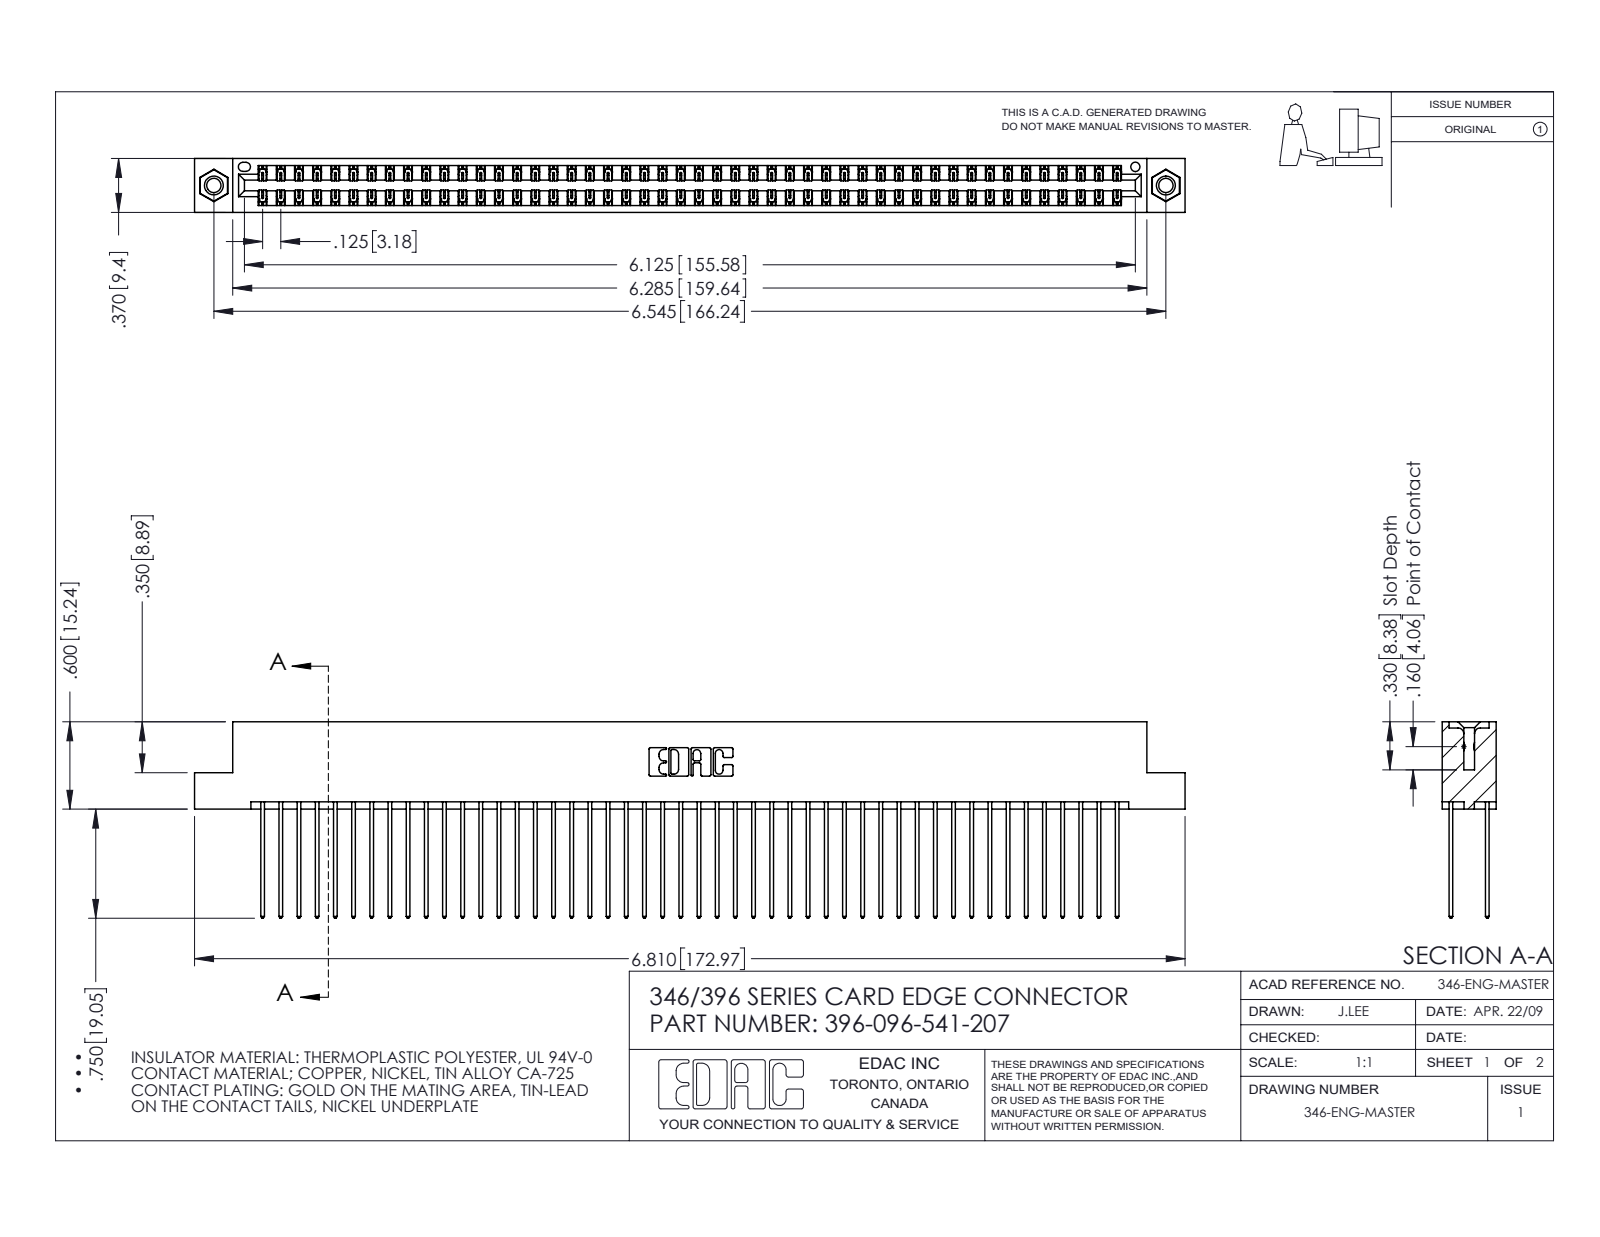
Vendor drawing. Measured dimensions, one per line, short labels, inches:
name: 396-096-541-207; 345-292-001_345-293-141; 345-250-001_345-250-005-103; 346 Part_Flush Mounting Lugs - 0.156 Dia-TI
written by: SolidWorks 2016 (CONFIG_CONTROL_DESIGN)
unit: in
bodies: 99 solids, 5174 faces (3468 planar, 1690 cylindrical, 16 other)
size: 6.81 × 1.35 × 0.37
volume: 1.065 in³; area: 41.47 in²
holes: 2× ⌀0.098, 2× ⌀0.125, 2× ⌀0.156, 1× ⌀0.064
bosses: 2× ⌀0.155
rounds: 144× R0.006, 96× R0.01, 22× R0.01, 6× R0.007, 6× R0.031, 3× R0.026, 2× R0.014, 2× R0.022
face distances: 0.048, 0.322, 0.25, 0.072, 0.298, 0.025, 0.37, 0.275, 0.225, 0.148
hole spacings: 0.246, 6.336, 6.545
